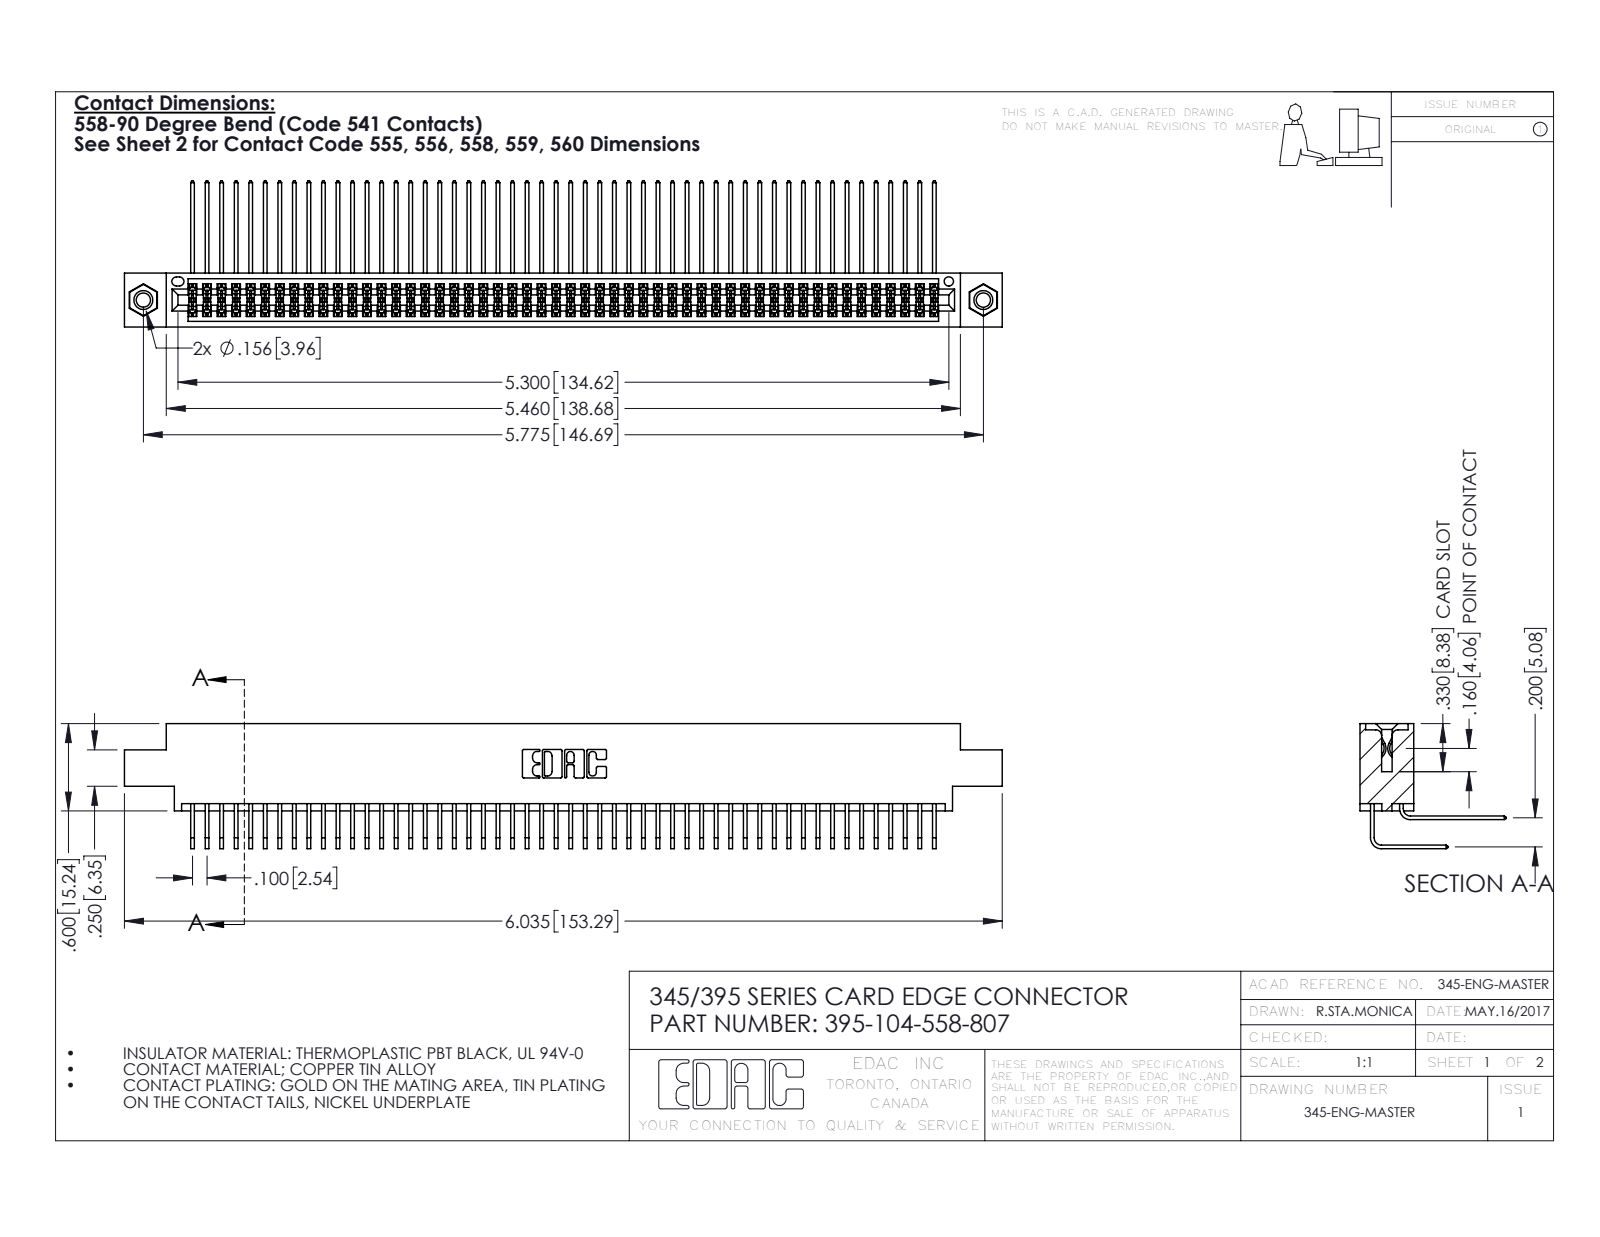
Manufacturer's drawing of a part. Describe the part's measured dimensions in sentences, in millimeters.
The part is named "345-292-001_558 559 Tail - 1; 345-250-001_345-250-005-103; 345-292-001_558 Tail - 2; 345 Part_0.170 Offset - 0.156 Dia-TI (+1 more)". Its 3-D file was written by "SolidWorks 2016 (CONFIG_CONTROL_DESIGN)". It is 107 solids with 5598 faces: 3756 planar, 1826 cylindrical and 16 other. Overall it measures 153.3 by 25.5 by 21.8 millimeters. Its volume is 15 500 cubic millimeters and its surface area 26 030 square millimeters. Round holes: 2 of diameter 2.5, 2 of diameter 3.2, 2 of diameter 4, 1 of diameter 1.6. Round bosses or shafts: 2 of diameter 3.9. Partial cylindrical surfaces (rounded edges, fillets, slot ends): 157 of radius 0.2, 22 of radius 0.3, 6 of radius 0.2, 6 of radius 0.8, 3 of radius 0.7, 2 of radius 0.4, 2 of radius 0.5, 2 of radius 0.6. The main face-to-face distances are 1.8, 7.6, 5.1, 9.4, 2.5, 6.9, 0.6, 5.7, 4.4, 0.6. The hole center spacings are 6.9, 140.7, 146.7.
